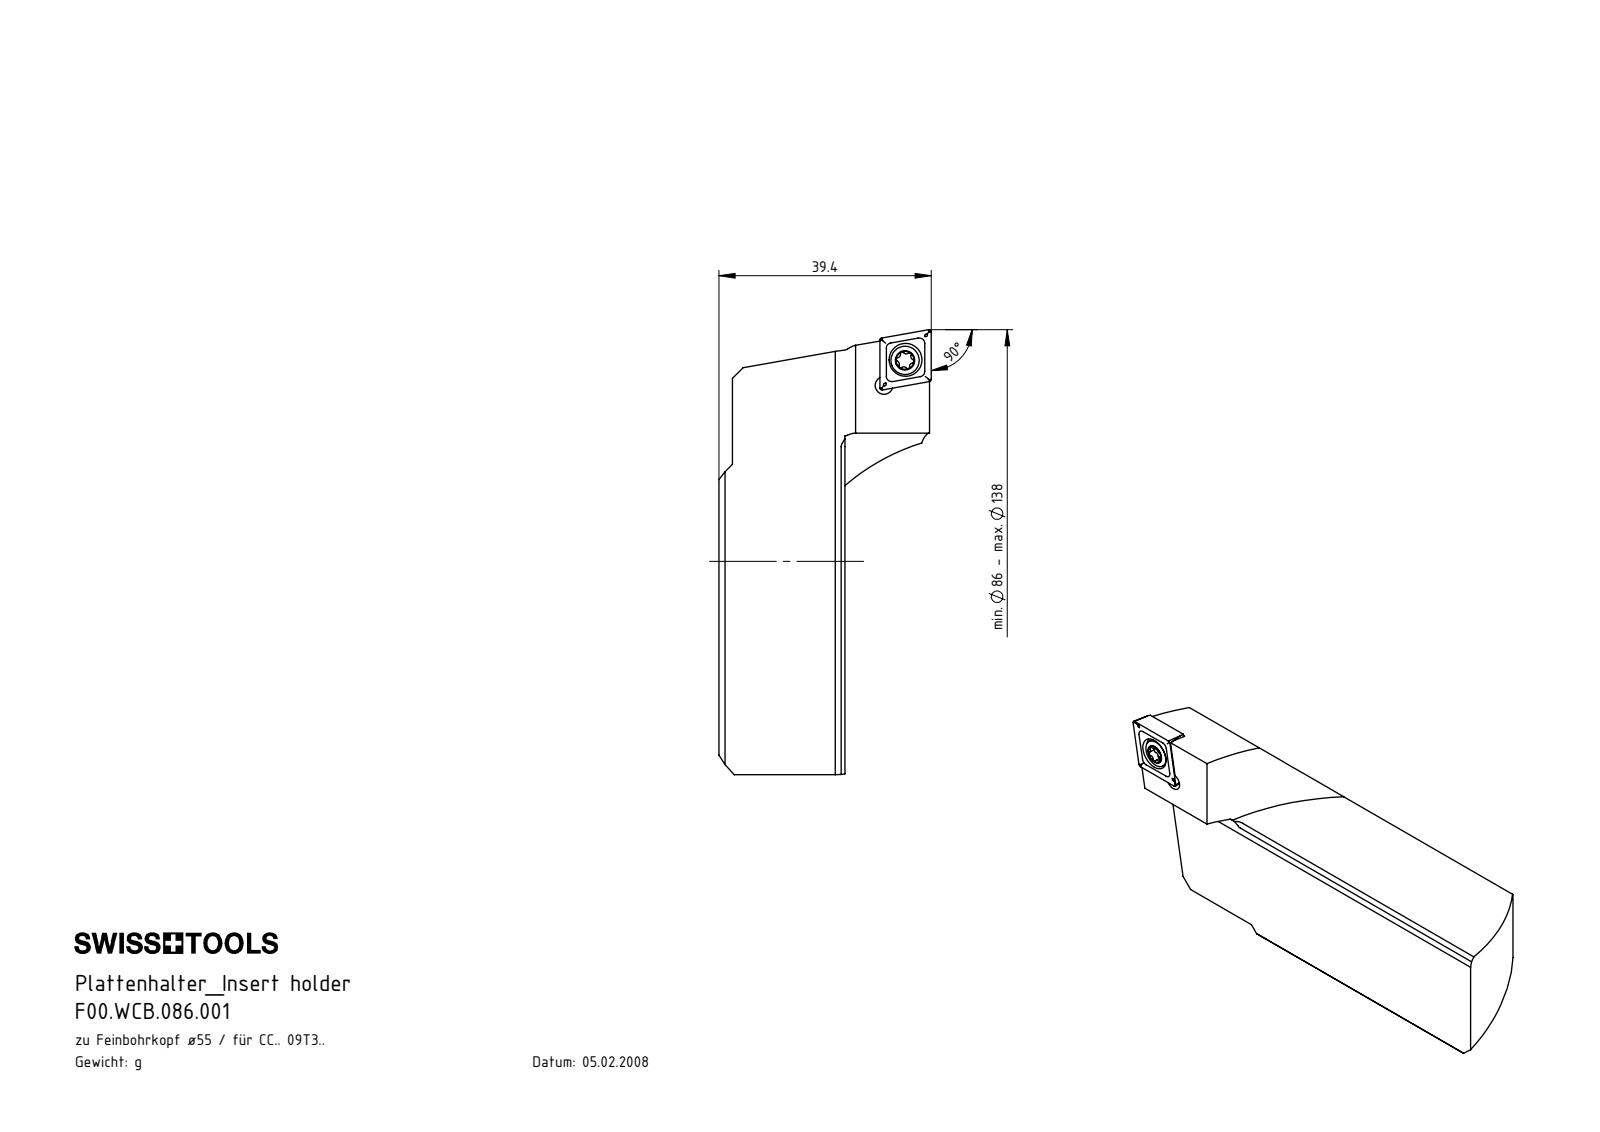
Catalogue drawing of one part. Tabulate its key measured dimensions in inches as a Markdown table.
| quantity | value |
| --- | --- |
| part name | CCMT09T304; F00-WCB.086.001_C; F00.WCB.086.001; WCB-ER2.001.009_A |
| STEP written by | SolidWorks 2017 (AUTOMOTIVE_DESIGN) |
| units | inches |
| bodies | 3 solids, 382 faces (226 planar, 39 cylindrical, 117 other) |
| overall size | 3.251 × 1.551 × 1.077 |
| volume | 2.048 in³ |
| surface area | 13.91 in² |
| round holes (diameter × count) | 0.13 × 2, 0.173 × 1, 0.24 × 1 |
| round bosses / shafts (diameter × count) | 0.207 × 1, 0.157 × 1 |
| partial cylindrical surfaces (radius × count) | 0.008 × 8, 0.013 × 6, 0.023 × 6, 1.575 × 3, 0.031 × 1 |
| main face-to-face distances | 0.094, 0.187, 0.839, 0.281, 0.375, 0.188, 0.281, 0.375, 0.469, 0.469 |
| hole center spacings | 0.239, 0.244 |
